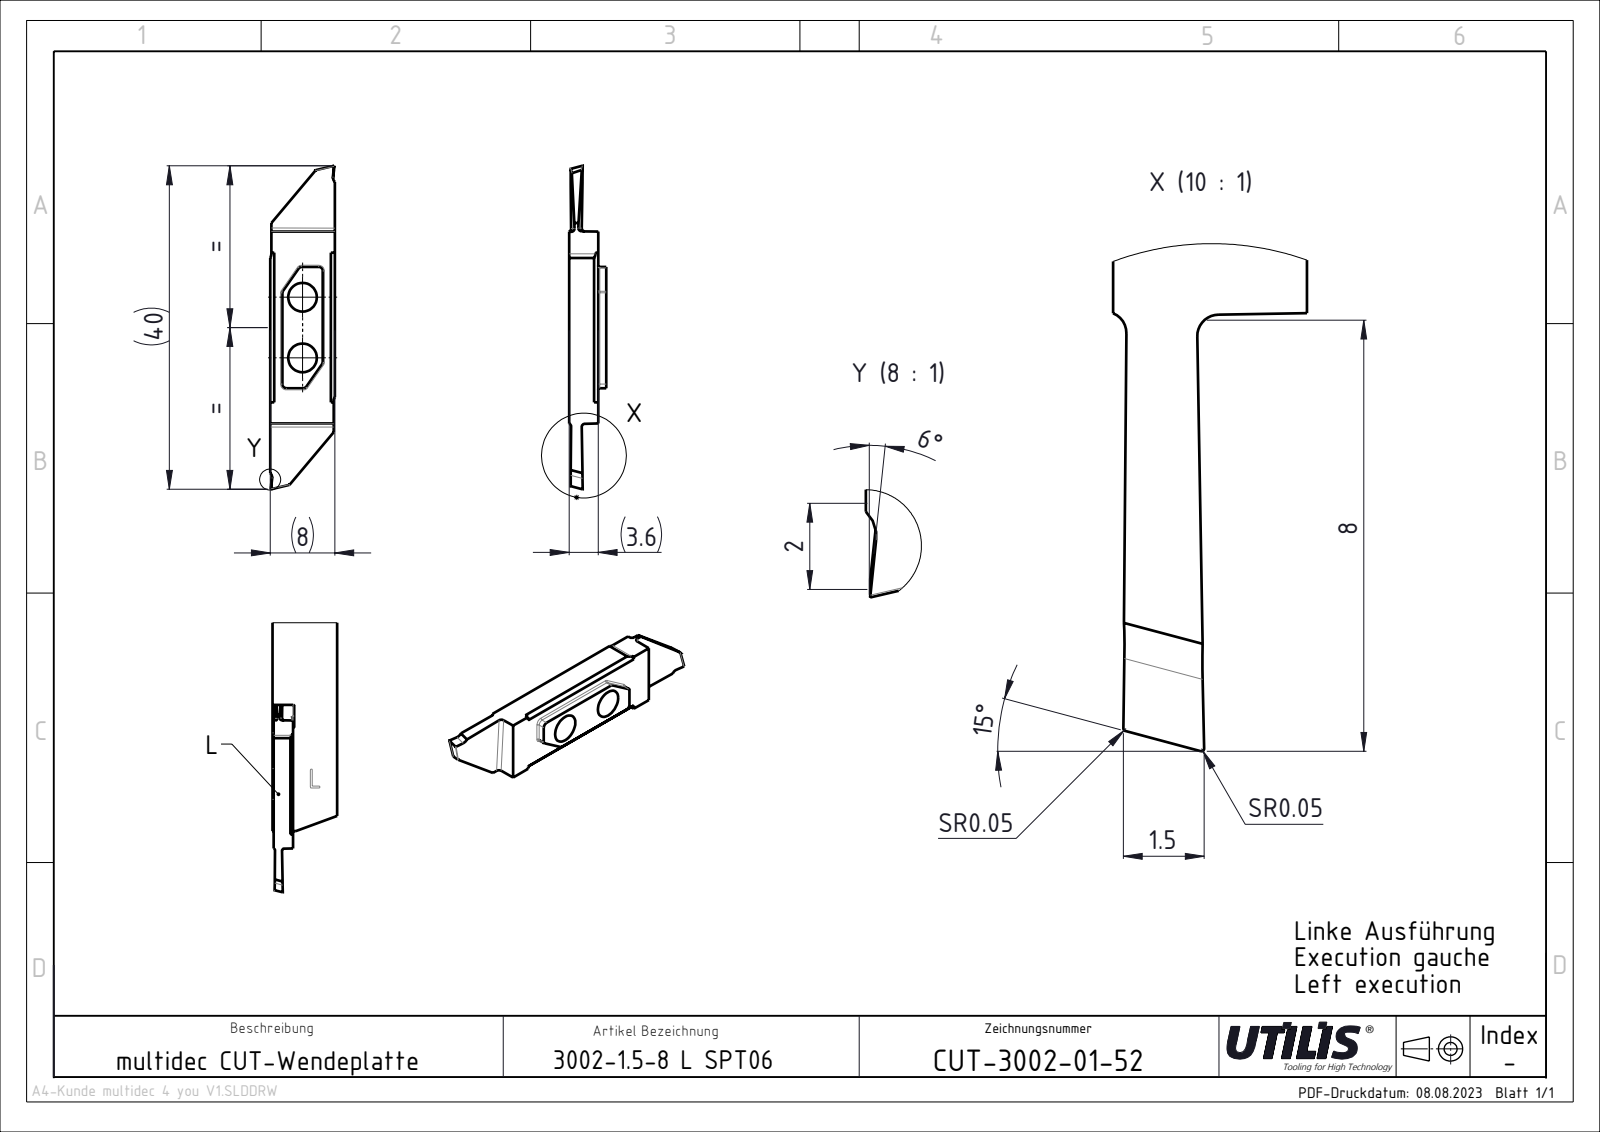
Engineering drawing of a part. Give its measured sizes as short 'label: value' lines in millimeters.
name: CUT-3002 SPT; ASME Y14.5
written by: SolidWorks 2023 SP4 || FormatWorks Professional (AP242_MANAGED_MODEL_BASED_3D_ENGINEERING_MIM_LF)
unit: mm
bodies: 1 solid, 36 faces (22 planar, 14 cylindrical, 0 other)
size: 40 × 8 × 3.6
volume: 723 mm³; area: 837 mm²
holes: 2× ⌀3.55
rounds: 4× R0.4, 2× R1
face distances: 3.6, 8, 7.85, 22.54, 7.7, 18.5
hole spacings: 7.49
